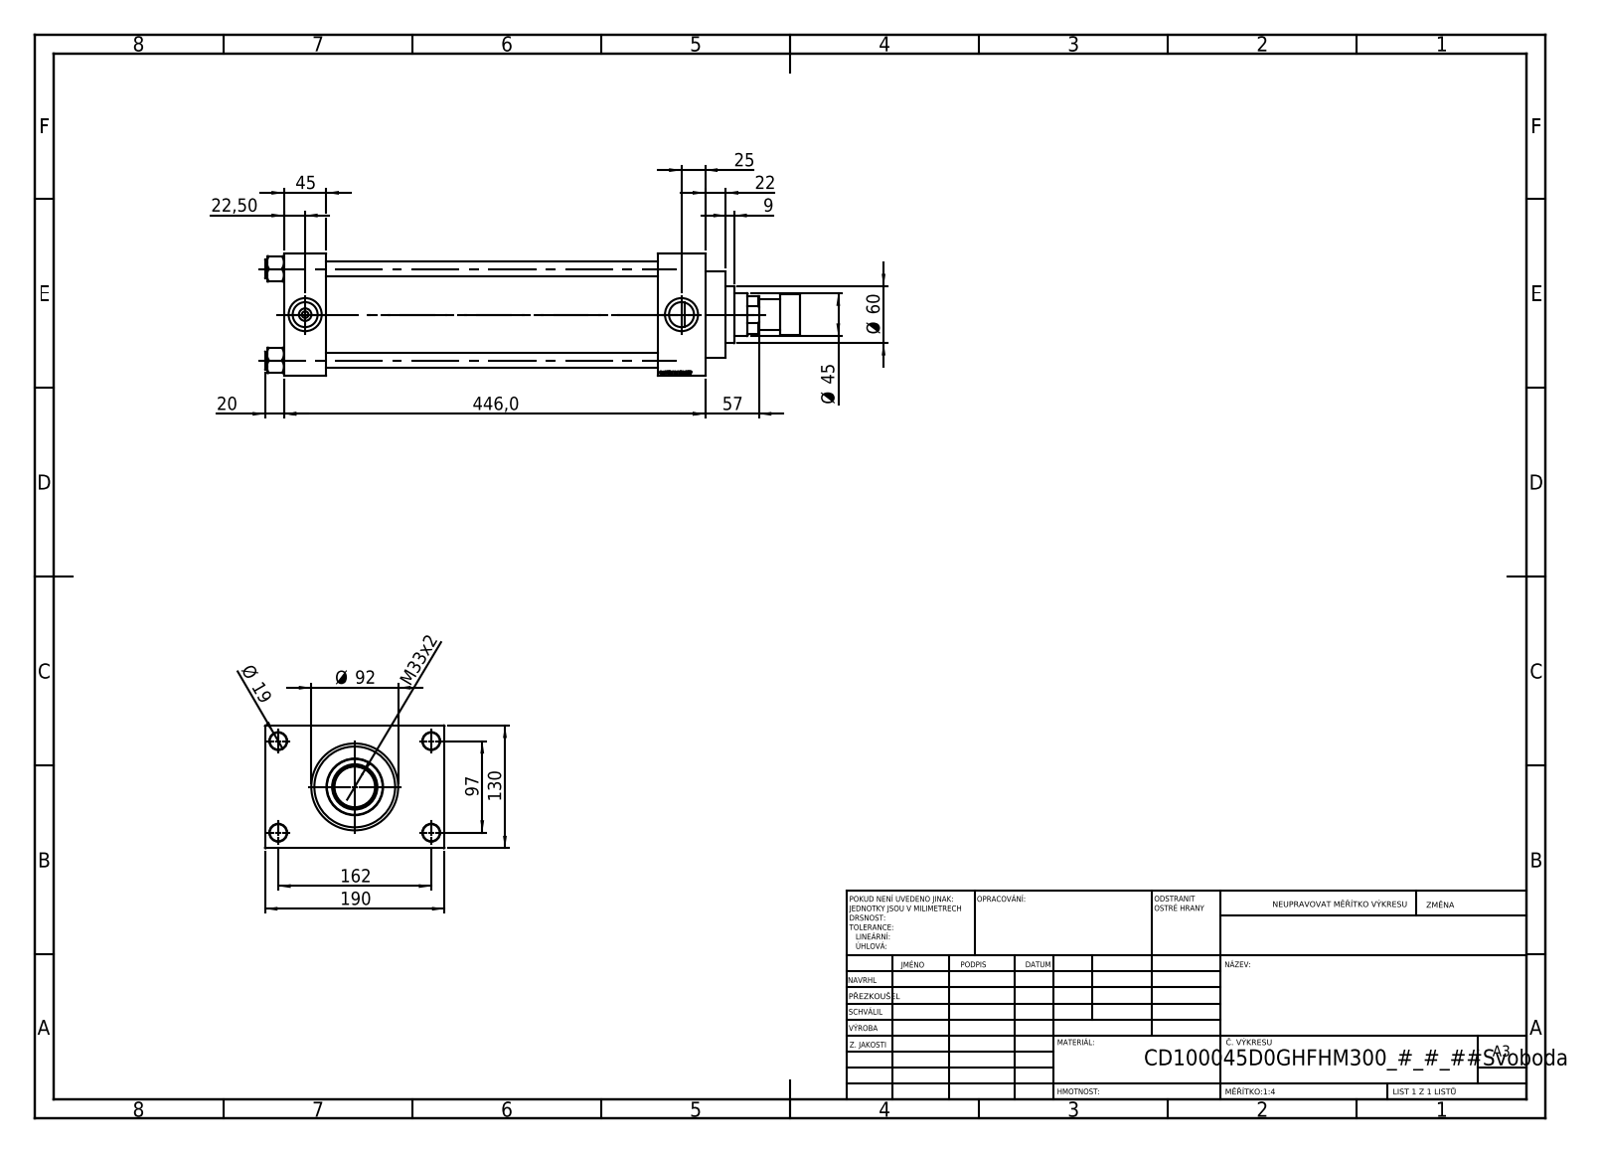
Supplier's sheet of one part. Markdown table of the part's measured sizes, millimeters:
| quantity | value |
| --- | --- |
| part name | V215CD_NUT_M5_D; V215CR_ROD_END_F; V215CD_D_Body; V215CD_D_TYCINKA (+2 more) |
| STEP written by | SolidWorks 2019 (CONFIG_CONTROL_DESIGN) |
| units | millimeters |
| bodies | 12 solids, 1164 faces (548 planar, 92 cylindrical, 524 other) |
| overall size | 567 × 190 × 130 |
| volume | 3 585 000 mm³ |
| surface area | 640 344 mm² |
| round holes (diameter × count) | 16 × 4, 18 × 4, 7 × 2, 26.44 × 2, 35 × 2, 31.5 × 1, 45 × 1, 48 × 1, 76 × 1, 85.5 × 1, 100 × 1 |
| round bosses / shafts (diameter × count) | 19 × 4, 106 × 1, 92 × 1, 60 × 1, 44 × 1, 33 × 1 |
| main face-to-face distances | 130, 45, 396, 351, 446, 401, 50, 30, 160, 96 |
| hole center spacings | 32.55, 68.52, 94.41, 96.9, 102.27, 129.45, 161.73, 97 |
